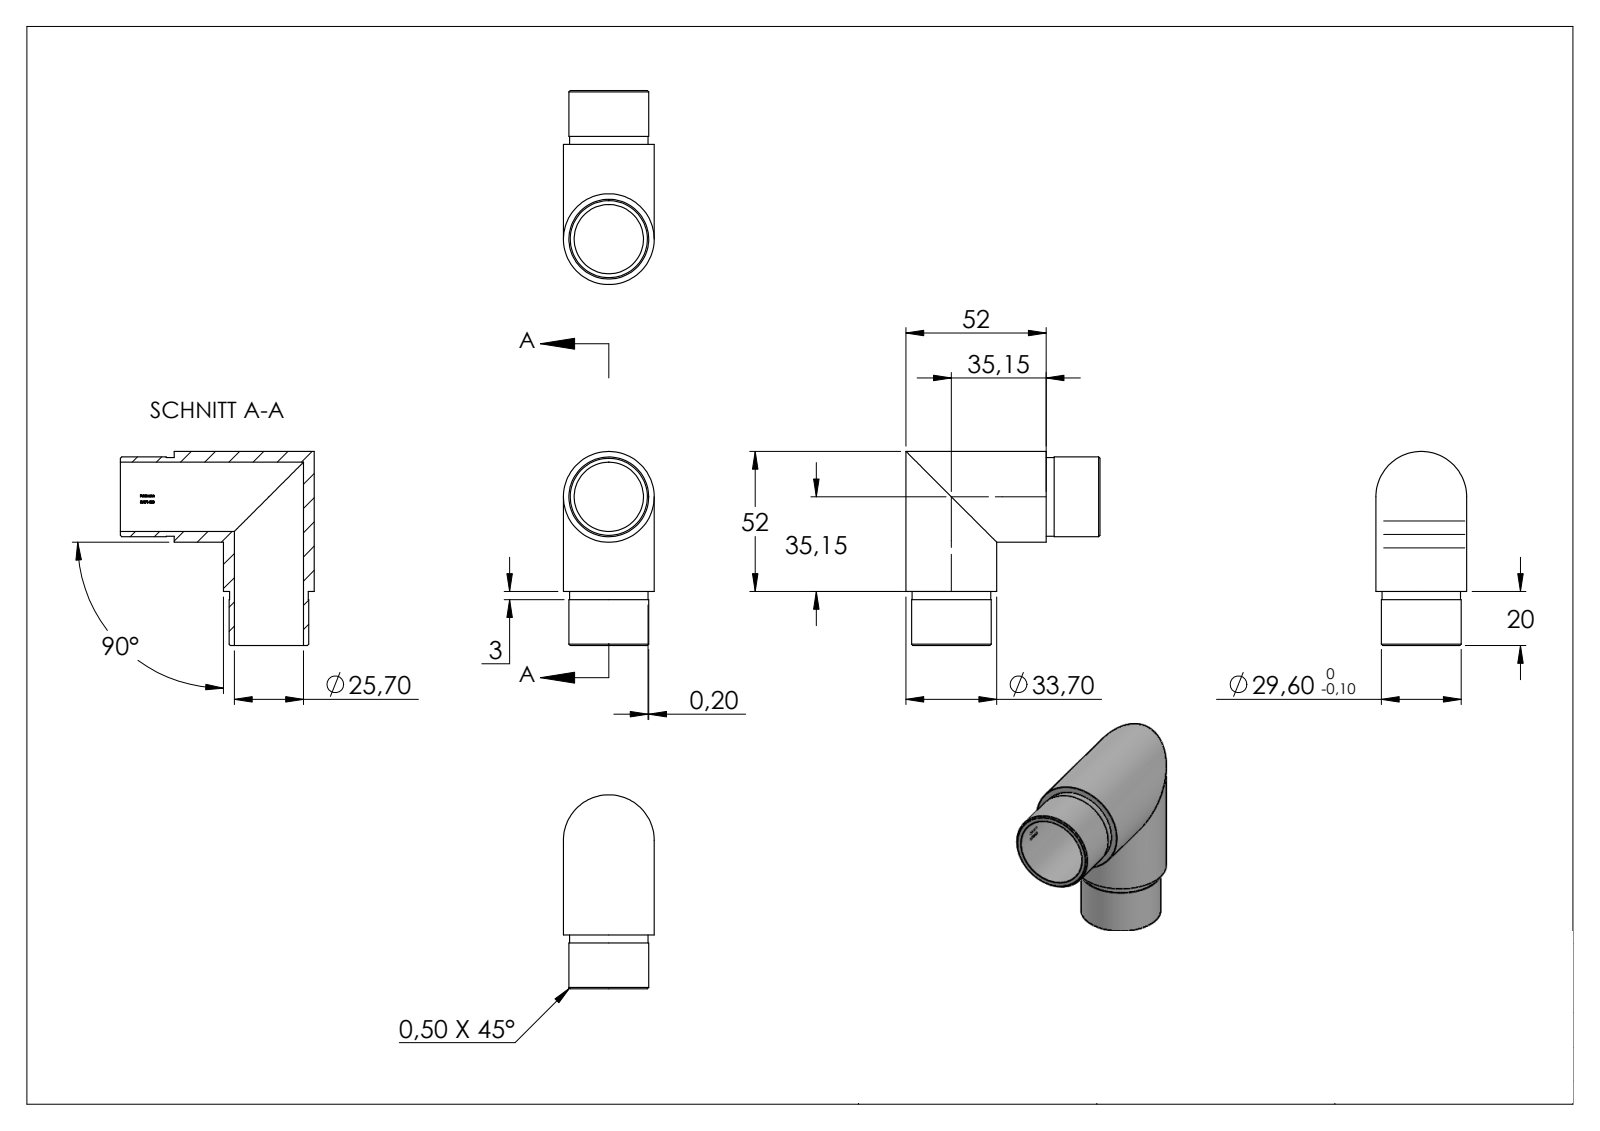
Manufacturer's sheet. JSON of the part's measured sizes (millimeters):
{"part_name": "56171-320", "step_written_by": "SolidWorks 2015 (CONFIG_CONTROL_DESIGN)", "units": "millimeters", "bodies": {"solids": 1, "faces": 226, "planar": 100, "cylindrical": 30, "other": 96}, "overall_size": [72, 72, 33.7], "volume_mm3": 32879, "surface_area_mm2": 20831, "round_holes": [[25.7, 2]], "round_bosses_or_shafts": [[33.7, 2], [29.6, 2], [29.2, 2]], "partial_cylinders_radius": [[12.95, 1]], "face_to_face_distances": [20, 17, 3, 0.83, 1.78, 0.76, 0.53, 2.59, 1.45, 1.22]}
